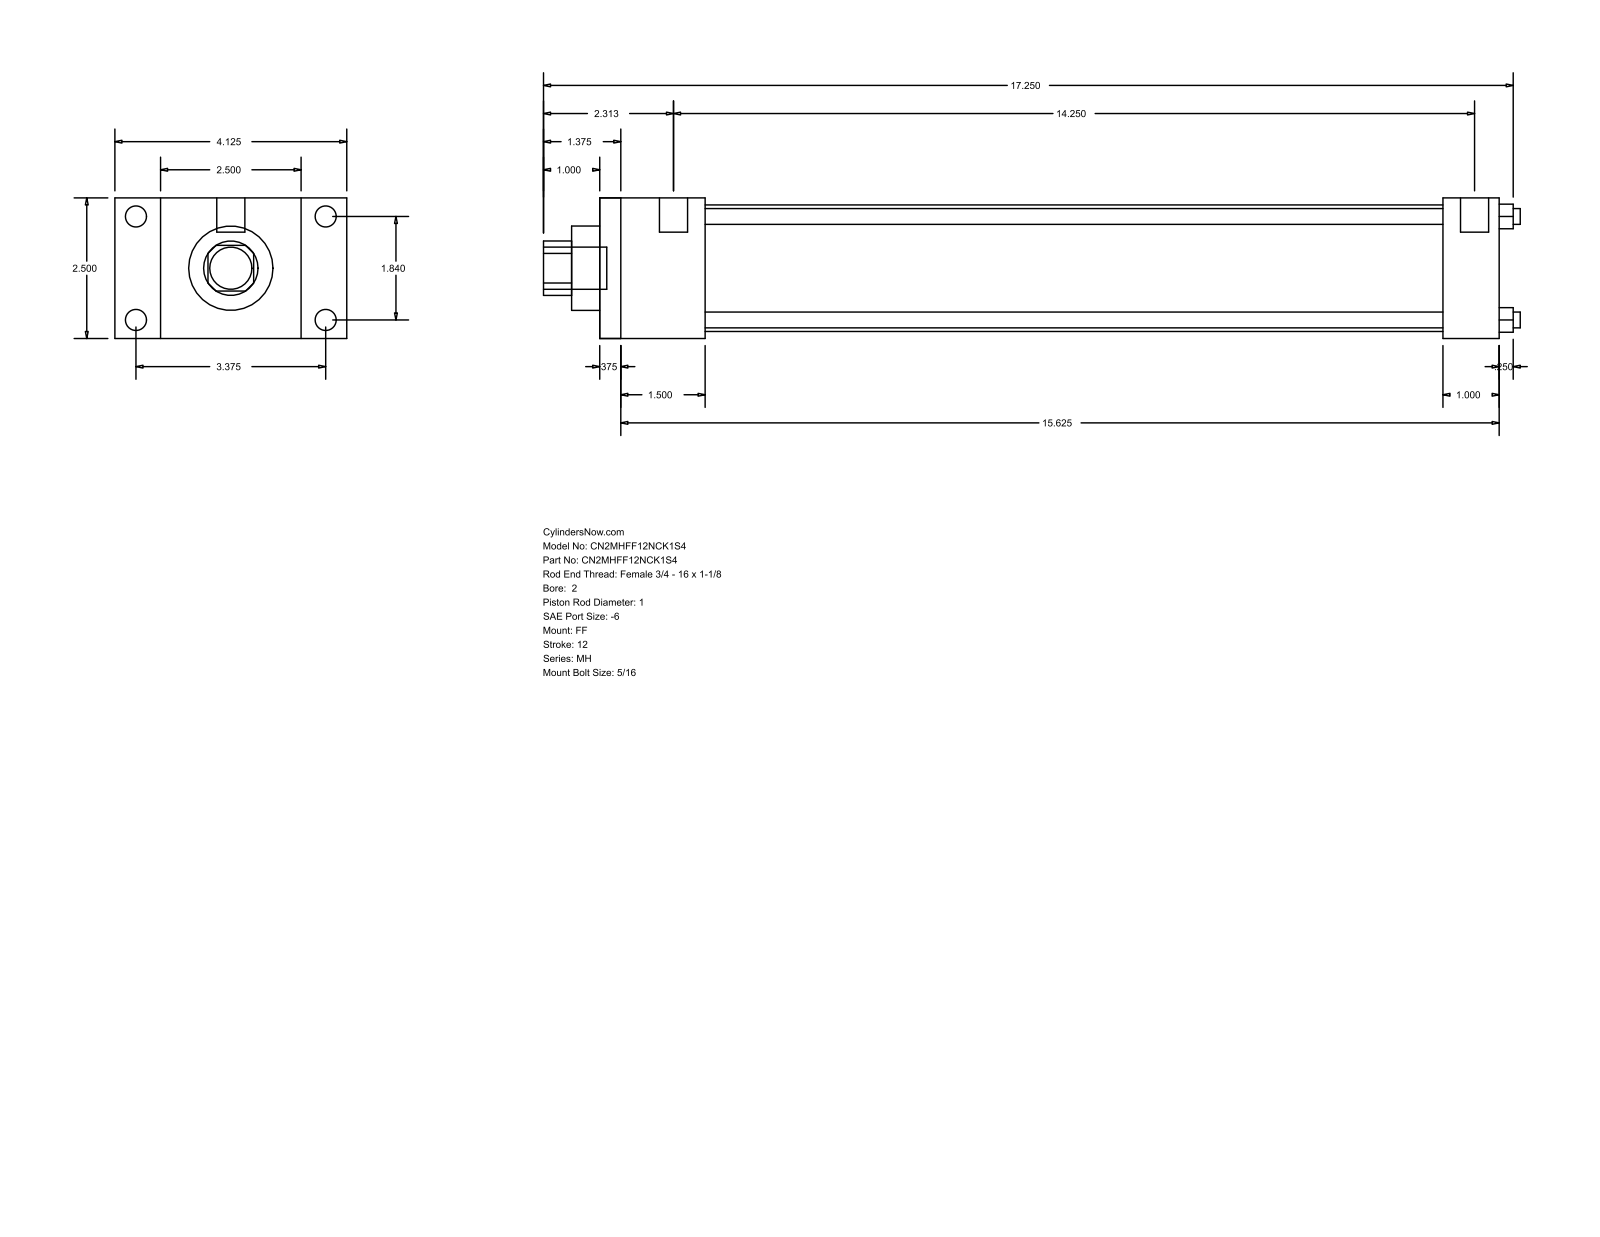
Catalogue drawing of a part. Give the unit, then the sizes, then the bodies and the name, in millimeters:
Units: millimetres
Overall size (bounding box): 441.32 × 104.78 × 63.5
Round holes (diameter × count): ⌀7.14 ×4, ⌀25.4 ×1, ⌀38.1 ×1, ⌀57.15 ×1
Round bosses / shafts (diameter × count): ⌀9.53 ×4, ⌀5.56 ×4, ⌀12.7 ×2, ⌀19.05 ×1
Partial cylindrical surfaces — rounded edges, fillets, slot ends (radius × count): R12.29 ×1
Main face-to-face distances: 63.5, 406.4, 9.52, 396.88, 20.64, 25.4, 47.63, 381, 38.11, 371.48
Hole centre spacings: 33.05, 46.74, 66.1
Bodies: 0 solids, 92 faces (64 planar, 28 cylindrical, 0 other)
Part name (STEP PRODUCT): MH_FF__0200_1
STEP written by: GSSL Pune (CONFIG_CONTROL_DESIGN)
